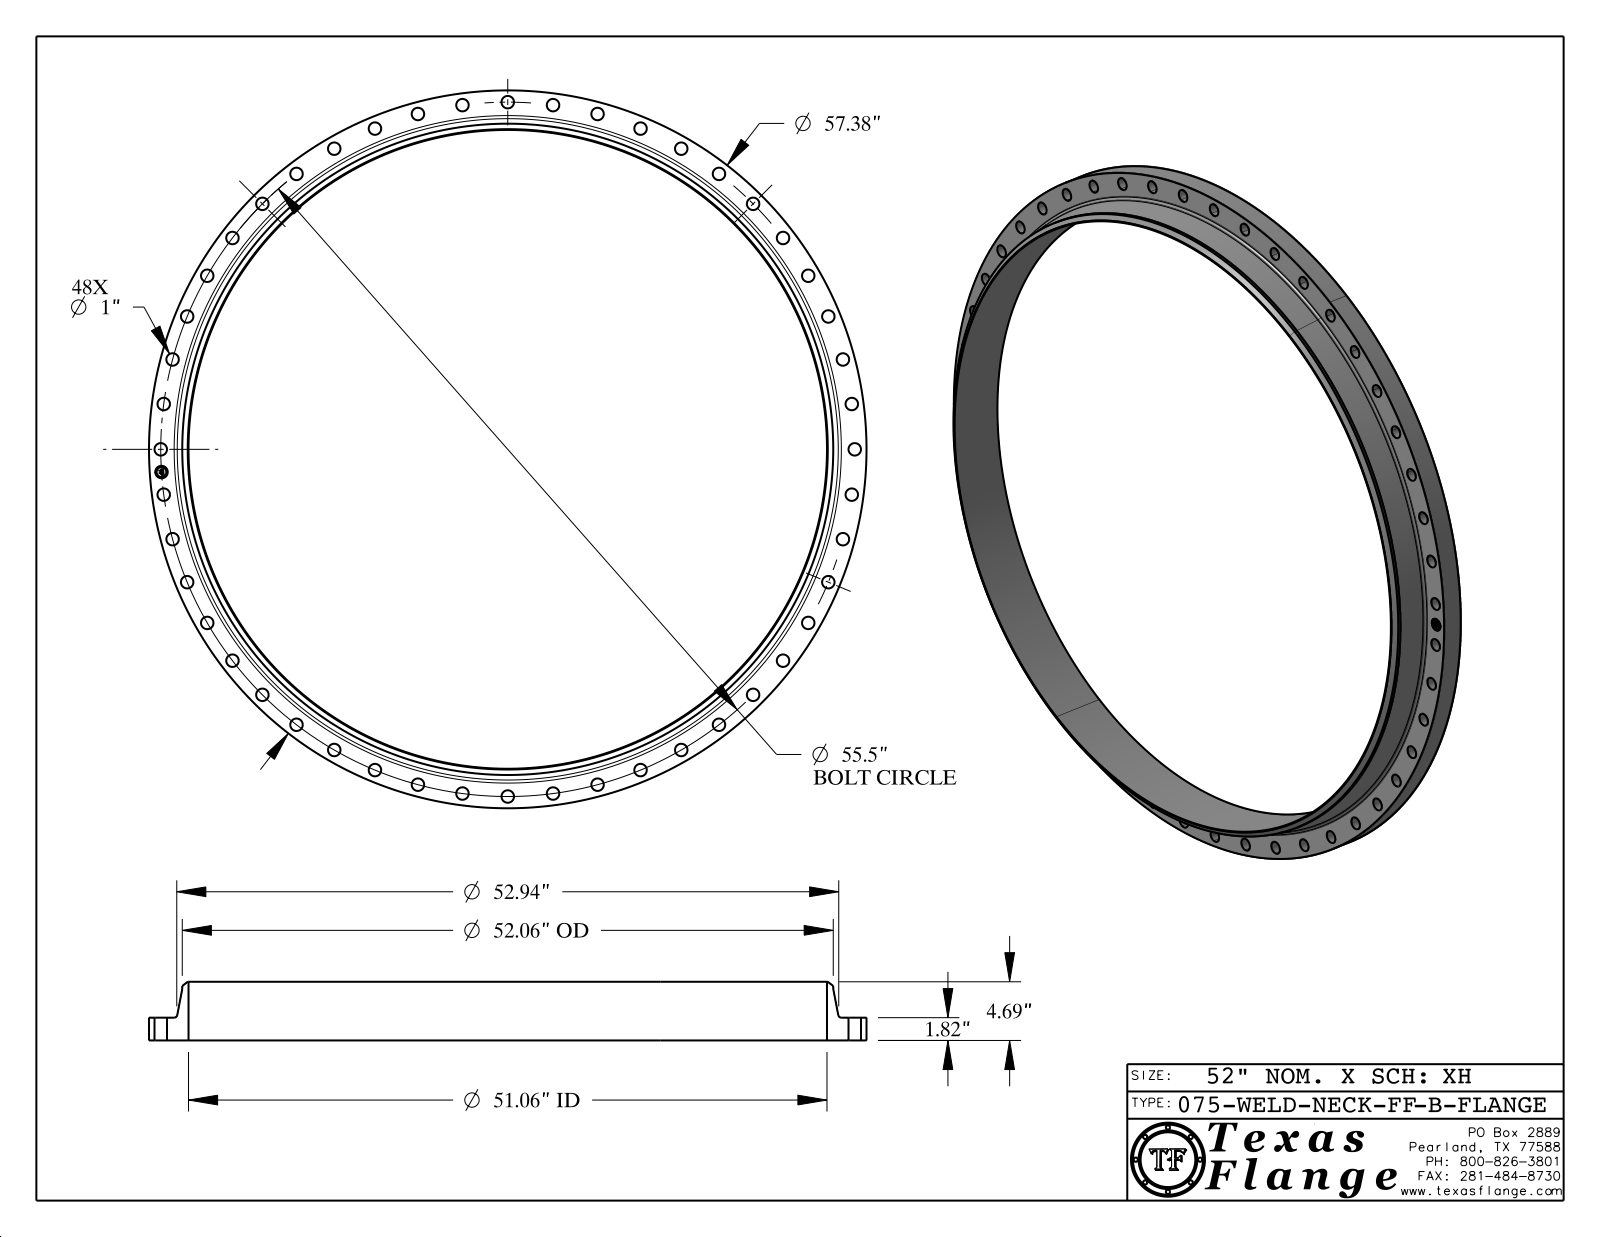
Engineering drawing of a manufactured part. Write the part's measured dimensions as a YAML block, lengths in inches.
part_name: "075-WELD-NECK-FF, Series B"
step_written_by: "CATIA V5 STEP AP214 (AUTOMOTIVE_DESIGN)"
units: inches
bodies: {solids: 1, faces: 496, planar: 368, cylindrical: 122, other: 6}
overall_size: [57.38, 57.38, 4.69]
volume: 1216
surface_area: 2715
round_holes:
  - {diameter: 1, count: 49}
  - {diameter: 51.06, count: 1}
round_bosses_or_shafts:
  - {diameter: 0.061, count: 8}
  - {diameter: 57.38, count: 1}
  - {diameter: 52.06, count: 1}
  - {diameter: 0.788, count: 1}
face_to_face_distances: [1.82, 4.69, 2.87, 1.805, 0.015, 2.885, 0.298, 0.293, 0.054, 0.193]
hole_center_spacings: [27.75, 7.244, 10.828, 55.025, 55.381, 3.63, 52.555, 54.434]
